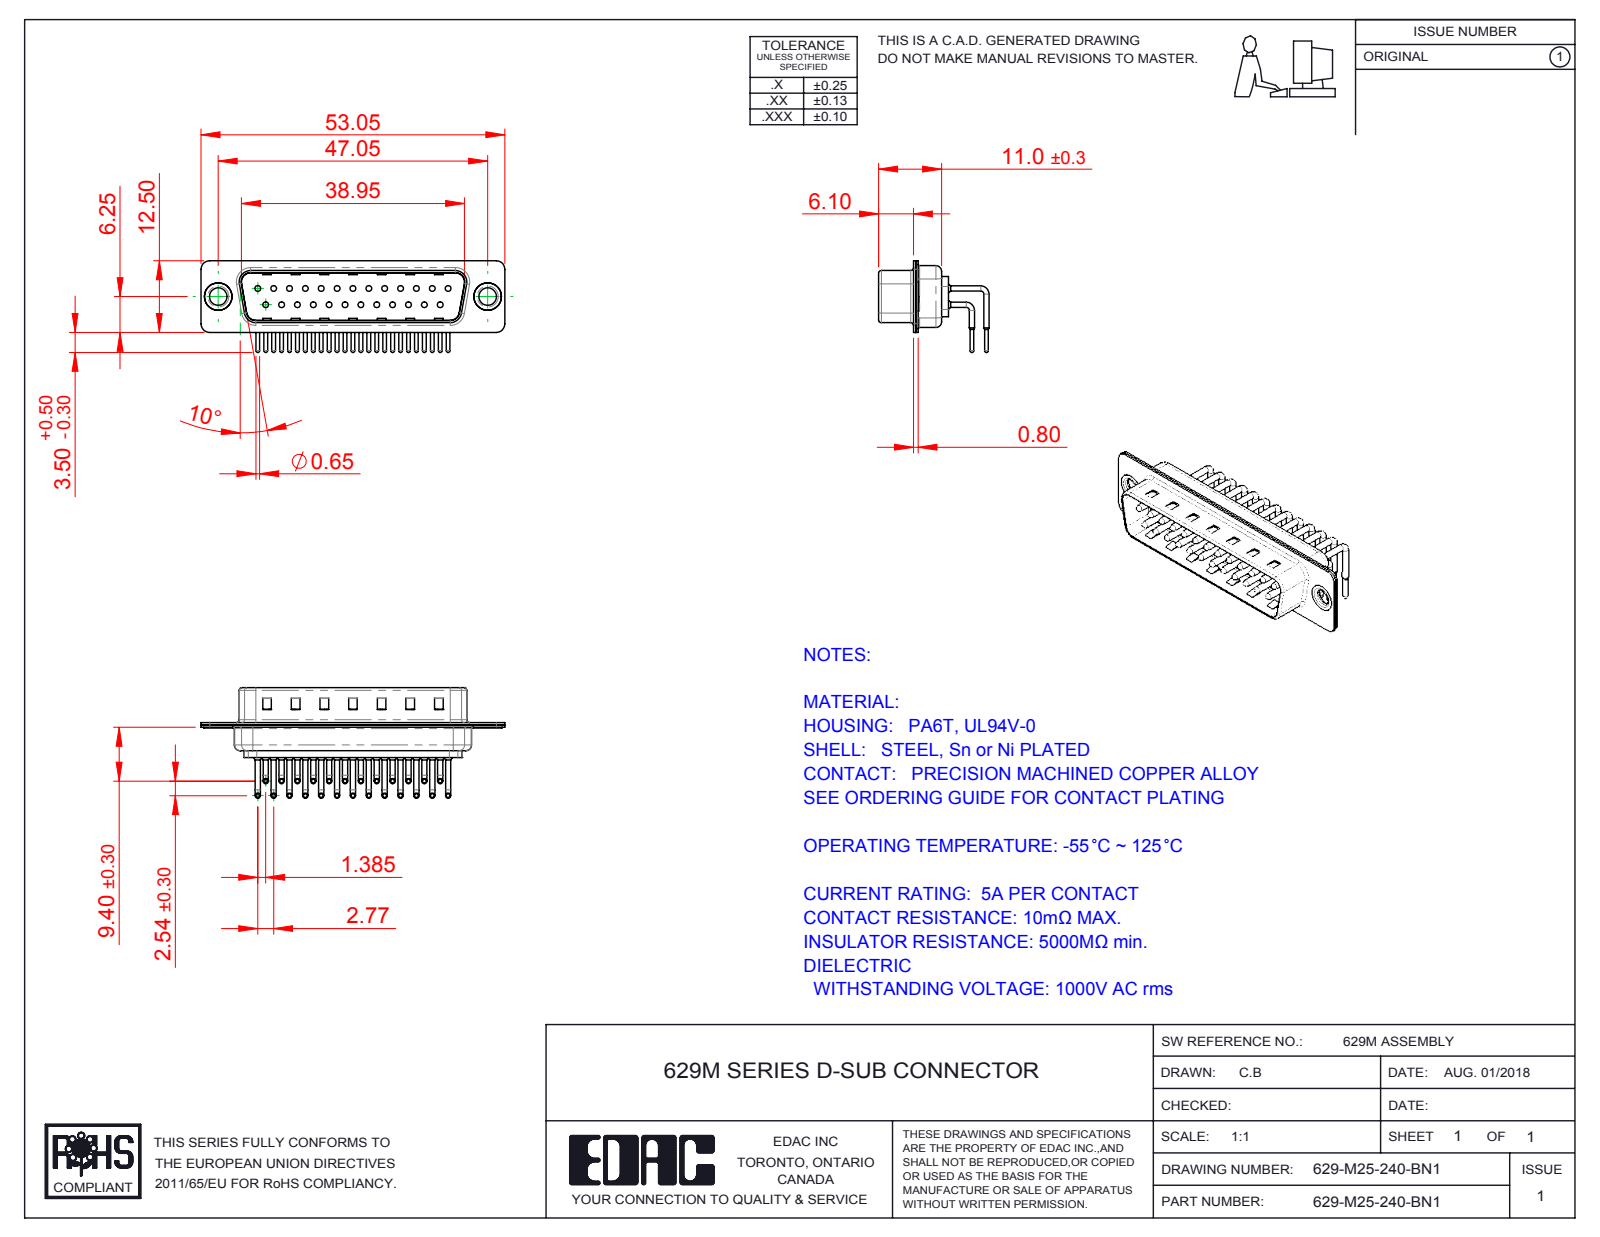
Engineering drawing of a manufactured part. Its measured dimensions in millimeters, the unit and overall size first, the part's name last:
Units: millimetres
Overall size (bounding box): 53.05 × 19.29 × 16
Round holes (diameter × count): ⌀1 ×25, ⌀1.7 ×25, ⌀2 ×25, ⌀3.05 ×2, ⌀4 ×2, ⌀4.8 ×2
Round bosses / shafts (diameter × count): ⌀0.9 ×50, ⌀1.5 ×25, ⌀0.65 ×25, ⌀5 ×2, ⌀4.9 ×2, ⌀3.55 ×2
Partial cylindrical surfaces — rounded edges, fillets, slot ends (radius × count): R1.01 ×25, R1.5 ×16, R2 ×12, R0.5 ×8, R1.6 ×8, R0.25 ×4, R0.6 ×4, R0.65 ×4
Main face-to-face distances: 0.4, 0.85, 9.55, 8.7, 1.25, 10.4, 1.5, 1.9, 0.35, 6.1
Hole centre spacings: 3.16, 2.77, 5.54, 8.31, 11.08, 13.85, 5.04, 7.49
Volume: 2 832 mm³ · Surface area: 7 610 mm²
Bodies: 30 solids, 3100 faces (1771 planar, 1021 cylindrical, 308 other)
Part name (STEP PRODUCT): 629M Housing_25 Contacts; 629-M25-240-BN1; 629M Shell Front_25 Contacts; 629M Shell Rear_25 Contacts (+3 more)
STEP written by: SolidWorks 2016 (CONFIG_CONTROL_DESIGN)
